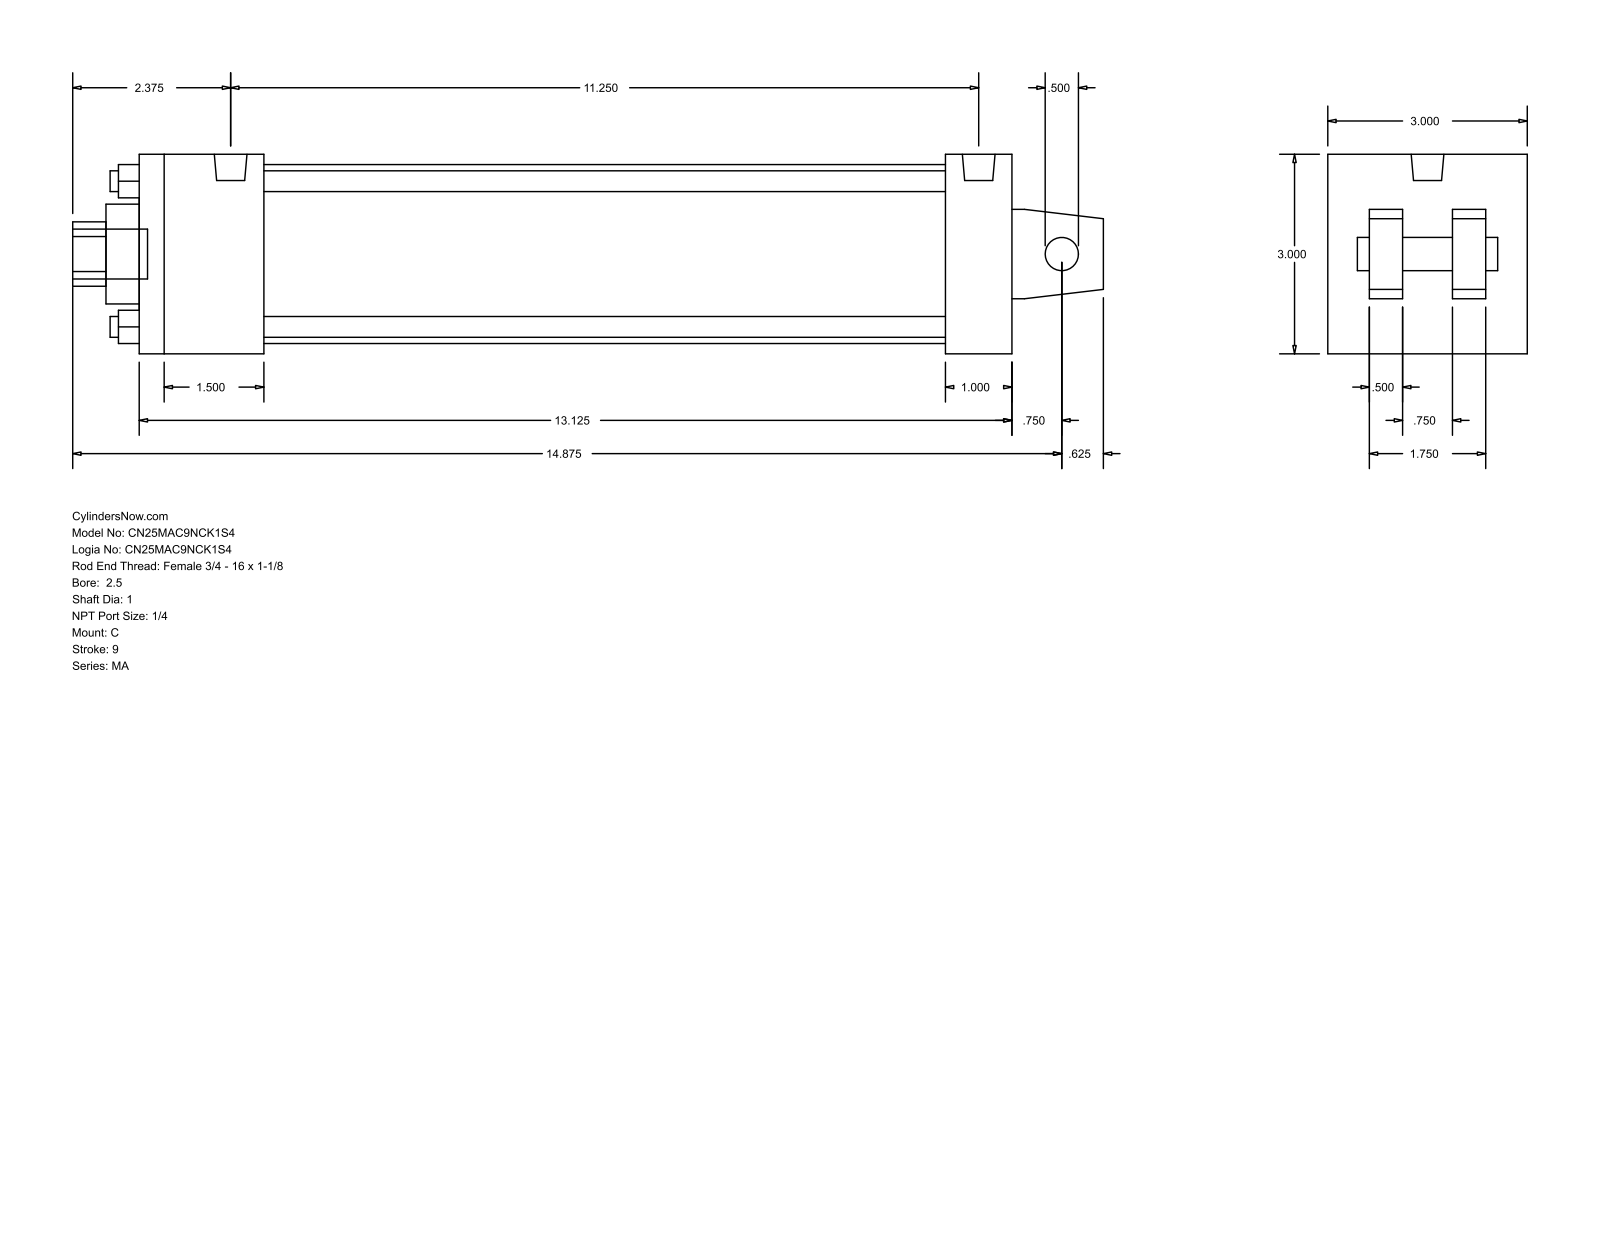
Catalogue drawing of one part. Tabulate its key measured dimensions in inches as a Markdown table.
| quantity | value |
| --- | --- |
| part name | MA_C__0250_1 |
| STEP written by | GSSL Pune (CONFIG_CONTROL_DESIGN) |
| units | inches |
| bodies | 0 solids, 103 faces (76 planar, 27 cylindrical, 0 other) |
| overall size | 15.5 × 3 × 3 |
| round holes (diameter × count) | 0.313 × 4, 0.5 × 1, 1 × 1, 1.5 × 1, 2.69 × 1 |
| round bosses / shafts (diameter × count) | 0.313 × 4, 0.492 × 2, 0.75 × 1 |
| partial cylindrical surfaces (radius × count) | 0.484 × 1 |
| main face-to-face distances | 3, 1.875, 13.125, 0.5, 0.625, 2.375, 1.125, 12.125, 10.25, 11.25 |
| hole center spacings | 1.548, 2.19, 3.097 |
